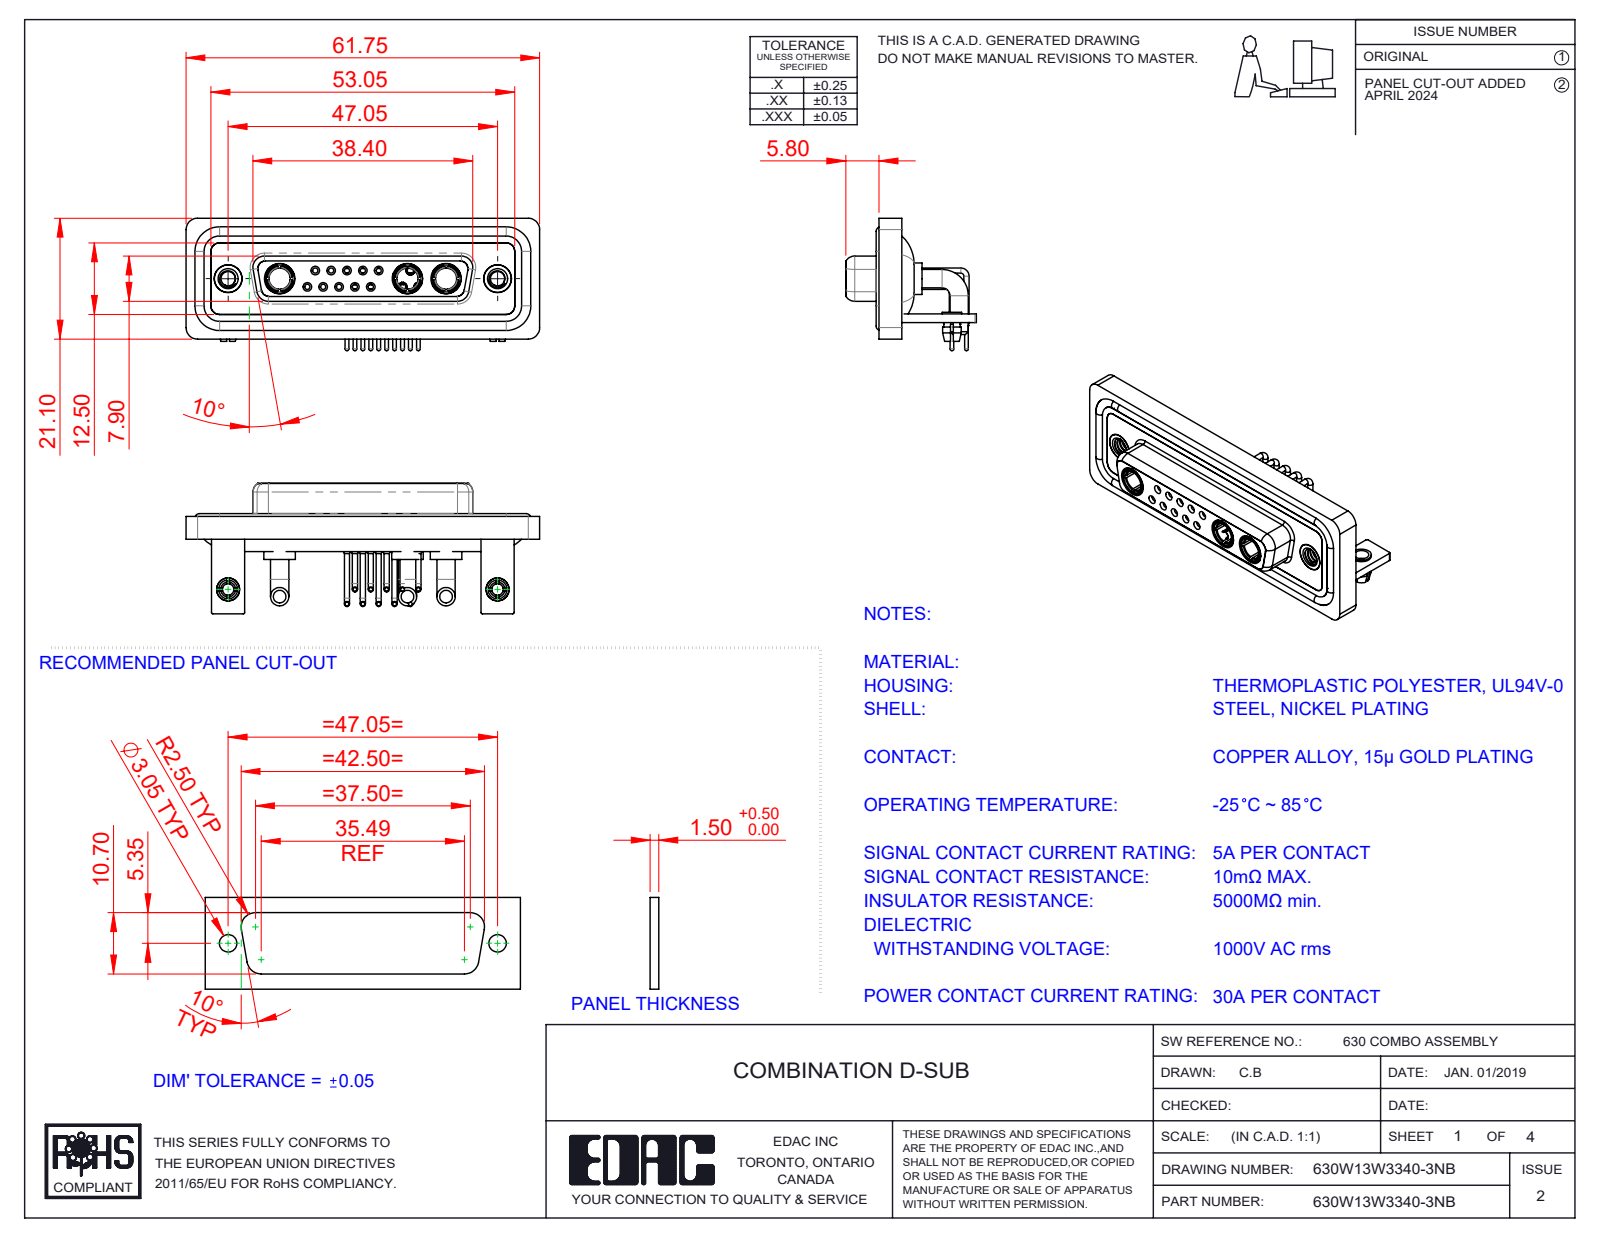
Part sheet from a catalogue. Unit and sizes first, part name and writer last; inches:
Units: inches
Overall size (bounding box): 2.431 × 0.91 × 0.898
Round holes (diameter × count): ⌀0.079 ×12, ⌀0.035 ×10, ⌀0.043 ×10, ⌀0.059 ×10, ⌀0.063 ×5, ⌀0.067 ×5, ⌀0.191 ×5, ⌀0.098 ×4, ⌀0.146 ×3, ⌀0.209 ×3, ⌀0.126 ×2, ⌀0.157 ×2
Round bosses / shafts (diameter × count): ⌀0.035 ×15, ⌀0.063 ×12, ⌀0.026 ×10, ⌀0.126 ×6, ⌀0.079 ×5, ⌀0.059 ×5, ⌀0.217 ×3, ⌀0.205 ×3
Partial cylindrical surfaces — rounded edges, fillets, slot ends (radius × count): R0.079 ×19, R0.059 ×18, R0.01 ×16, R0.053 ×8, R0.063 ×8, R0.02 ×5, R0.024 ×4, R0.026 ×4
Main face-to-face distances: 0.016, 0.071, 0.114, 0.146, 0.059, 0.161, 0.043, 0.055, 0.063, 0.122
Hole centre spacings: 0.124, 0.109, 0.218, 0.198, 0.327, 0.198, 0.295, 0.436
Volume: 0.546 in³ · Surface area: 23.72 in²
Bodies: 27 solids, 1284 faces (410 planar, 547 cylindrical, 327 other)
Part name (STEP PRODUCT): 630Combo Contact Row 2_50 Contacts; 630Combo Shell Front_25 Contacts; 630Combo Stabilizer Bracket_50 Contacts; 630Combo Board Lock_50 Contacts (+7 more)
STEP written by: SolidWorks 2023 (CONFIG_CONTROL_DESIGN)
